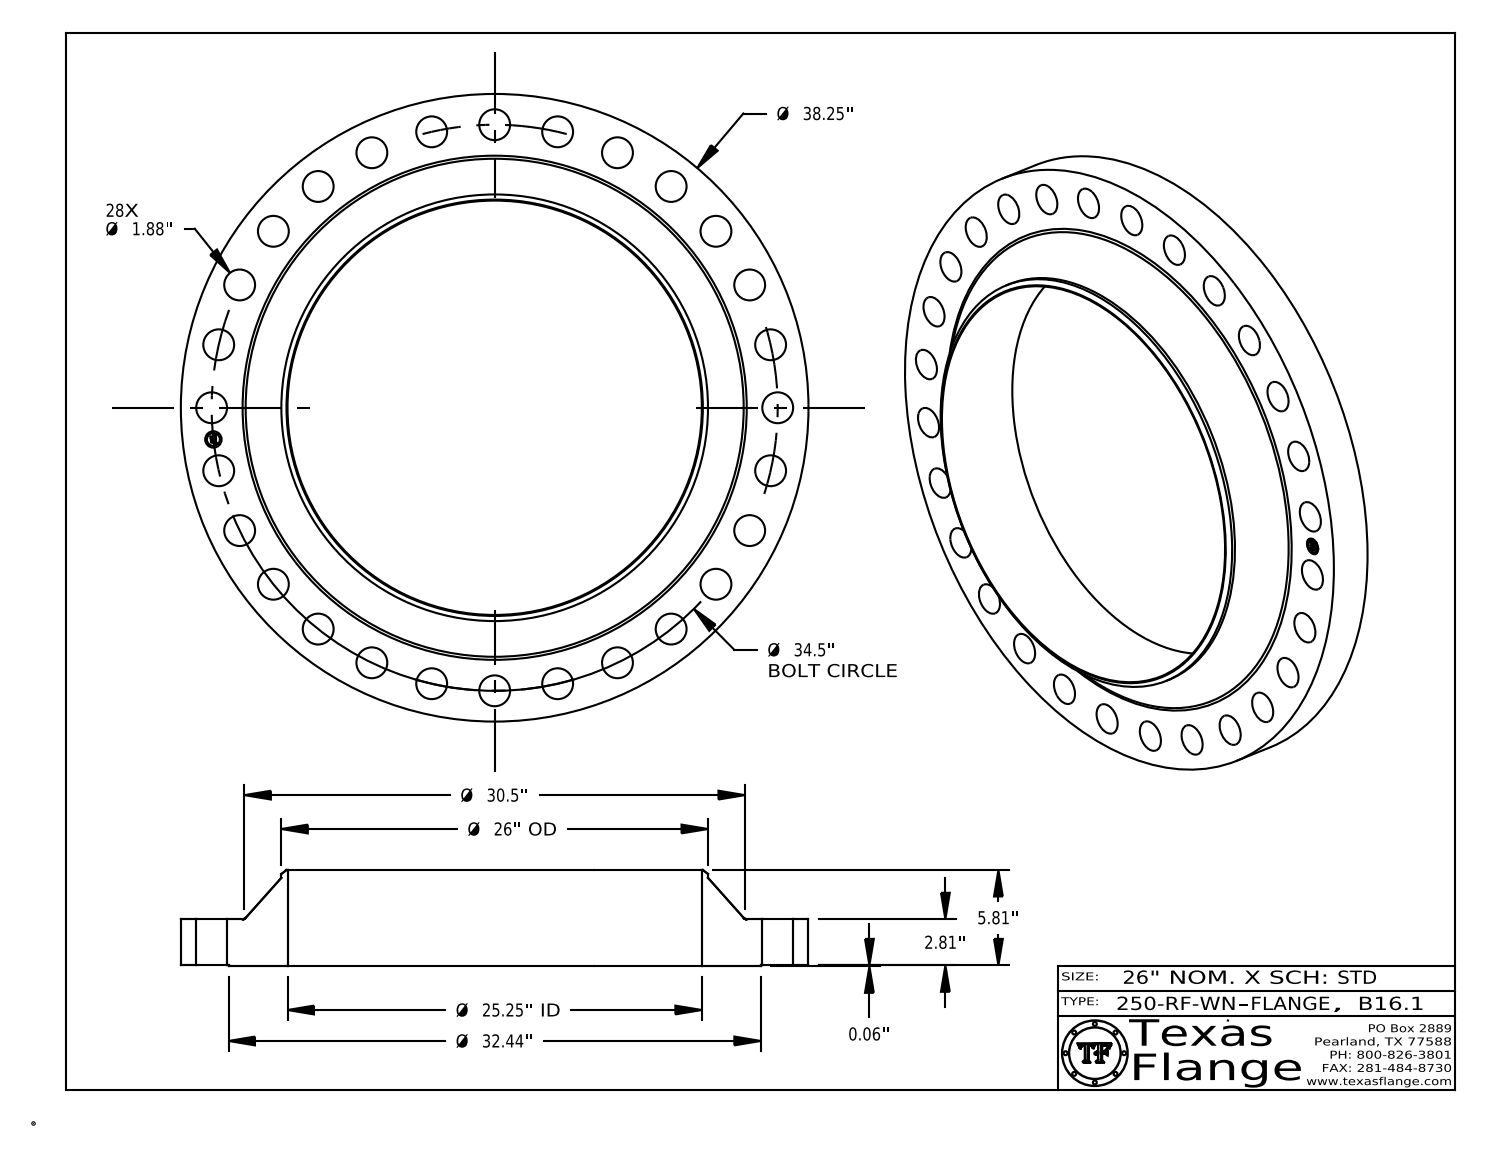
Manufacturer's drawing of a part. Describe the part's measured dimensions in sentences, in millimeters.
The part is named "250-RF-WN, B16.1". Its 3-D file was written by "CATIA V5 STEP AP203 (CONFIG_CONTROL_DESIGN)". It is 1 solid with 459 faces: 369 planar, 84 cylindrical and 6 other. Overall it measures 971.55 by 971.55 by 149.16 millimeters. Its volume is 32 070 000 cubic millimeters and its surface area 1 639 000 square millimeters. Round holes: 28 of diameter 47.75, 1 of diameter 25.4, 1 of diameter 641.35. Round bosses or shafts: 8 of diameter 1.54, 1 of diameter 971.55, 1 of diameter 823.98, 1 of diameter 660.4, 1 of diameter 20.01. The main face-to-face distances are 72.96, 1.59, 71.37, 149.16, 147.57, 76.2, 0.38, 72.58, 70.99, 76.58. The hole center spacings are 438.15, 685.12, 870.79, 380.21, 466.22, 827.12, 854.33, 289.42.
